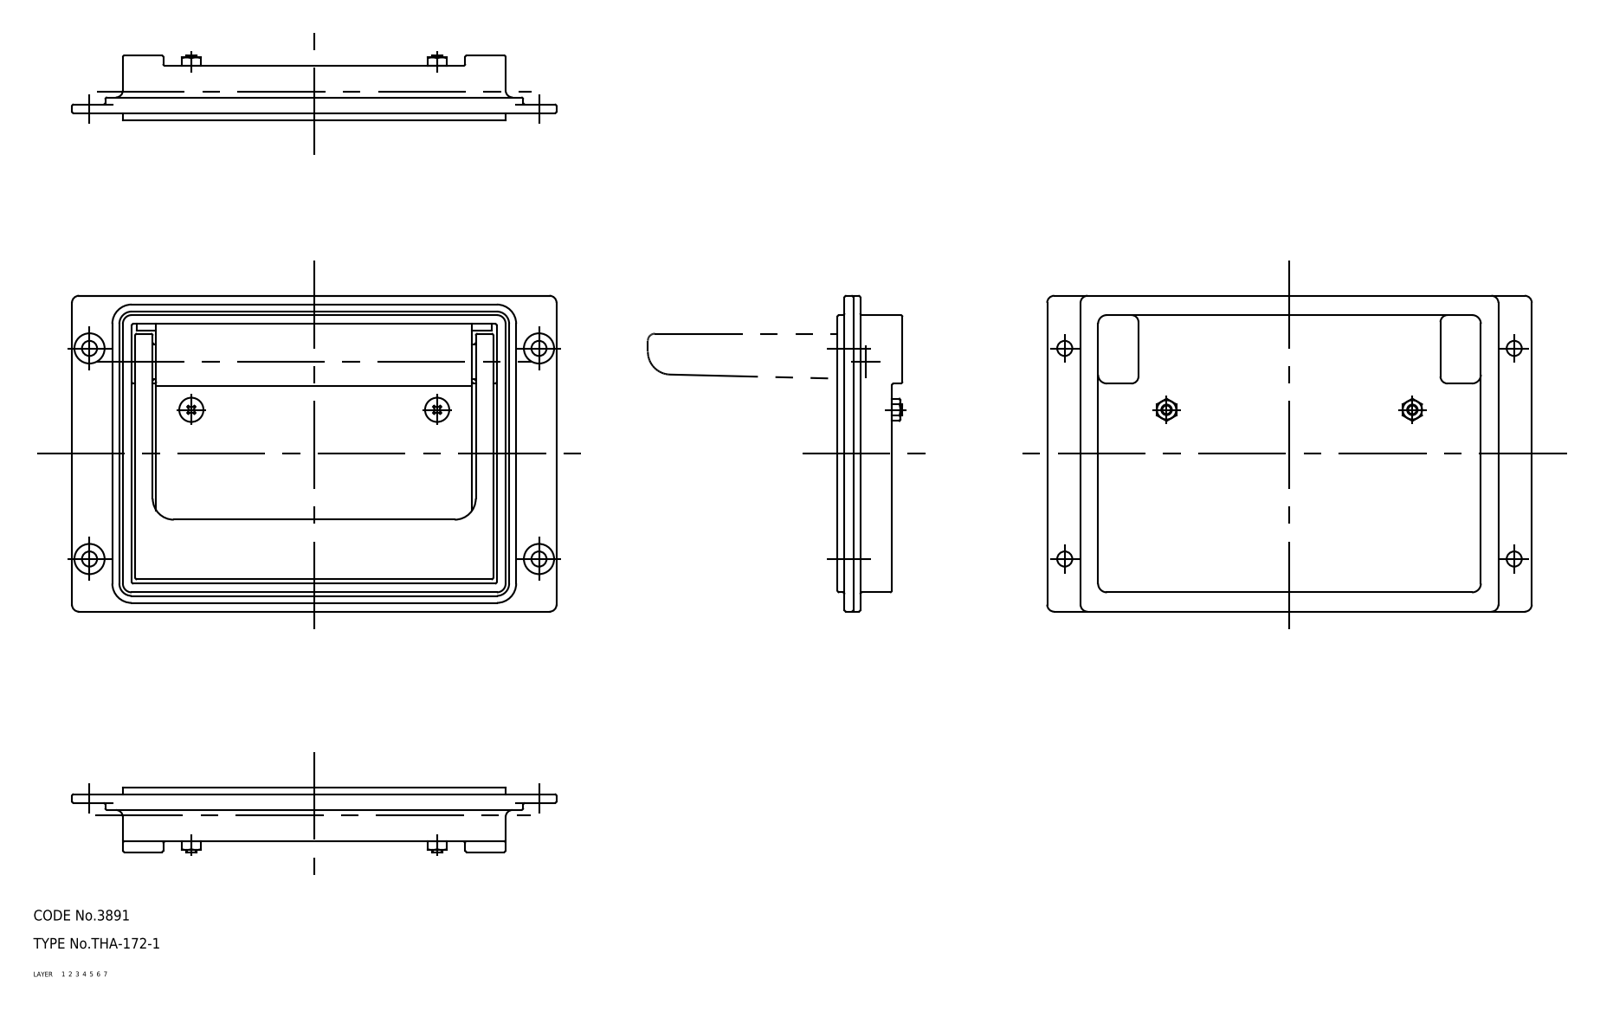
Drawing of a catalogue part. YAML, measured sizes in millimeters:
part_name: "nut; screw; washer; grip (+4 more)"
step_written_by: "CADfix (AUTOMOTIVE_DESIGN)"
units: millimeters
bodies: {solids: 10, faces: 427, planar: 0, cylindrical: 0, other: 427}
overall_size: [138, 90, 18.5]
volume: 85655
surface_area: 65007
